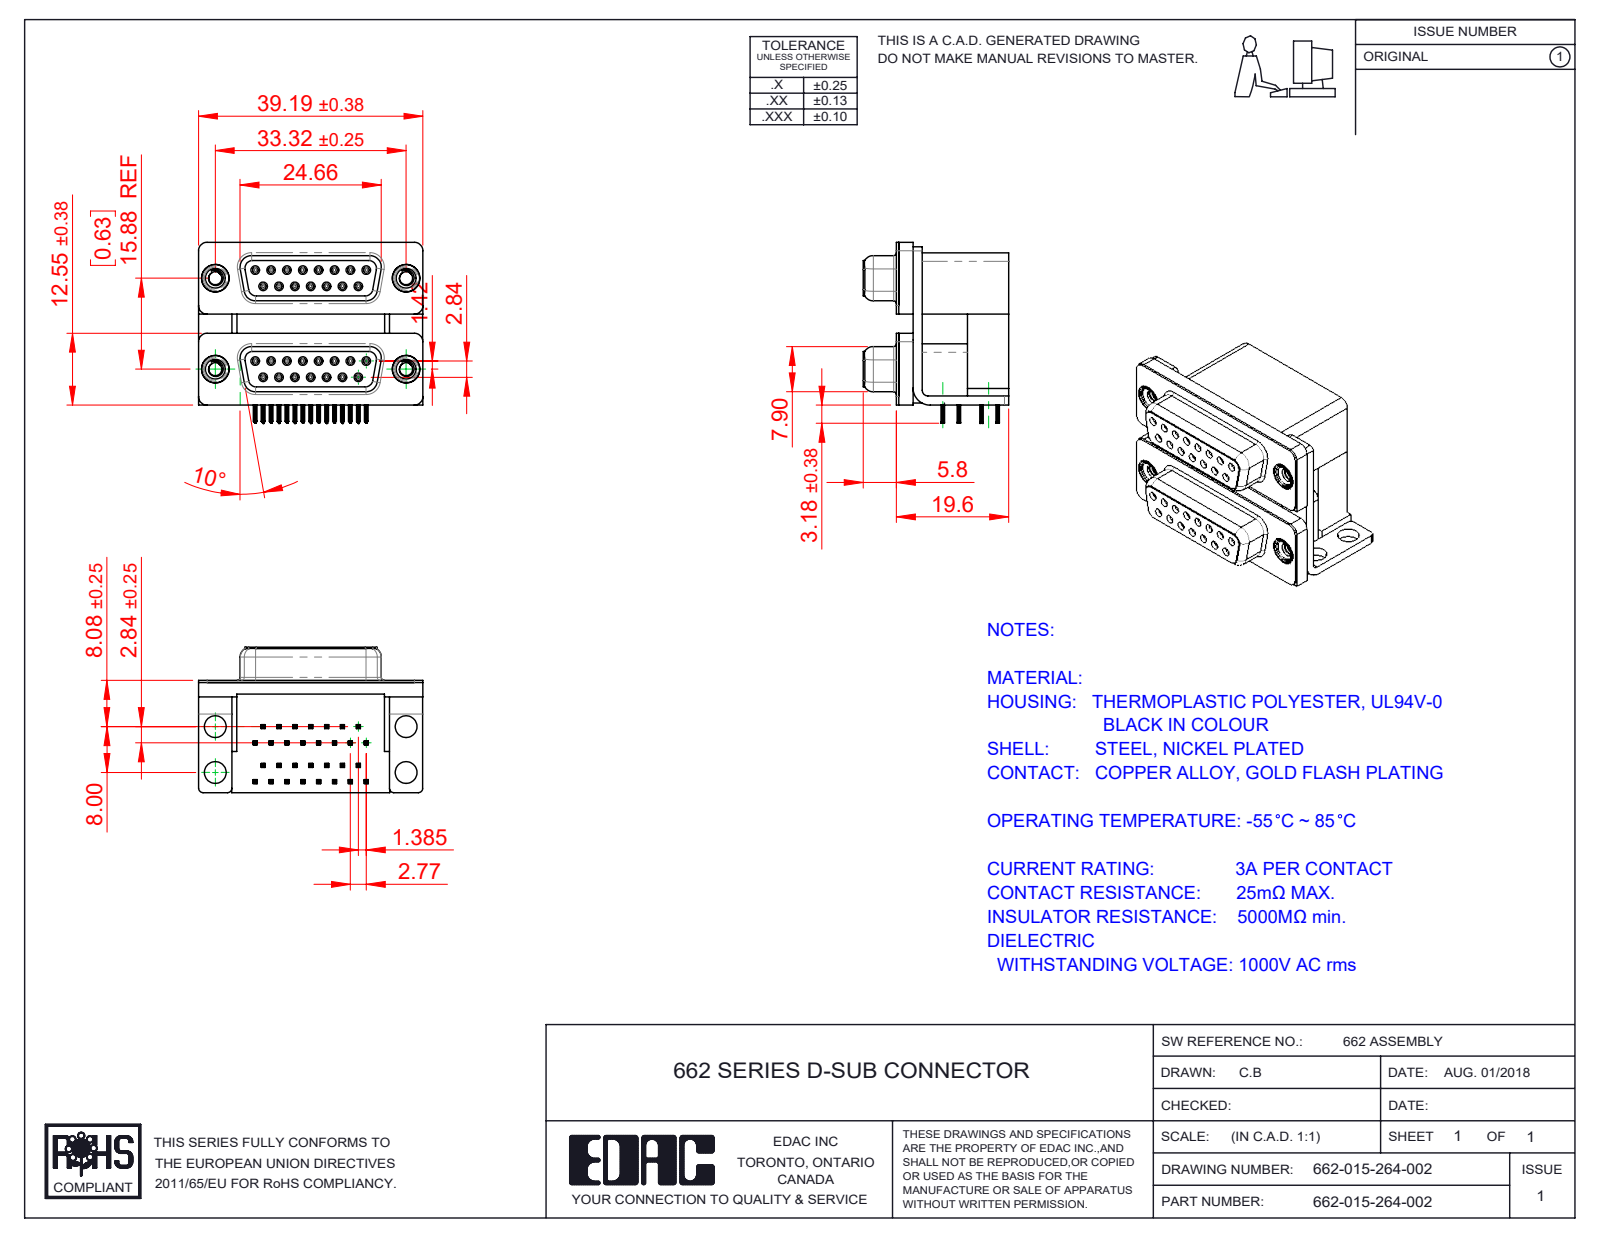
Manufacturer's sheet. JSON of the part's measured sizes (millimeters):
{"part_name": "662 Threaded Rivet_4-40; 662 Housing Lower_15 Contacts; 662 Contact Bottom Lower; 662 Contact Top Lower (+7 more)", "step_written_by": "SolidWorks 2020 (CONFIG_CONTROL_DESIGN)", "units": "millimeters", "bodies": {"solids": 41, "faces": 4862, "planar": 2196, "cylindrical": 1174, "other": 1492}, "overall_size": [39.19, 31.61, 25.4], "volume_mm3": 15357, "surface_area_mm2": 17299, "round_holes": [[0.8, 30], [0.9, 30], [2.26, 4], [3.5, 4], [3.8, 4], [4, 4], [4.8, 4], [5, 4]], "round_bosses_or_shafts": [[1.2, 30], [4.9, 4], [4.75, 4], [3.9, 4]], "partial_cylinders_radius": [[0.1, 240], [0.15, 120], [0.35, 60], [0.34, 30], [1.35, 16], [1.5, 15], [0.28, 14], [0.5, 8]], "face_to_face_distances": [0.4, 19.2, 16.7, 2.5, 10.7, 15.88, 2.9, 7.2, 9.5, 12], "hole_center_spacings": [3.16, 16.12, 2.77, 16.82, 5.54, 8.31, 15.88, 17.92]}
